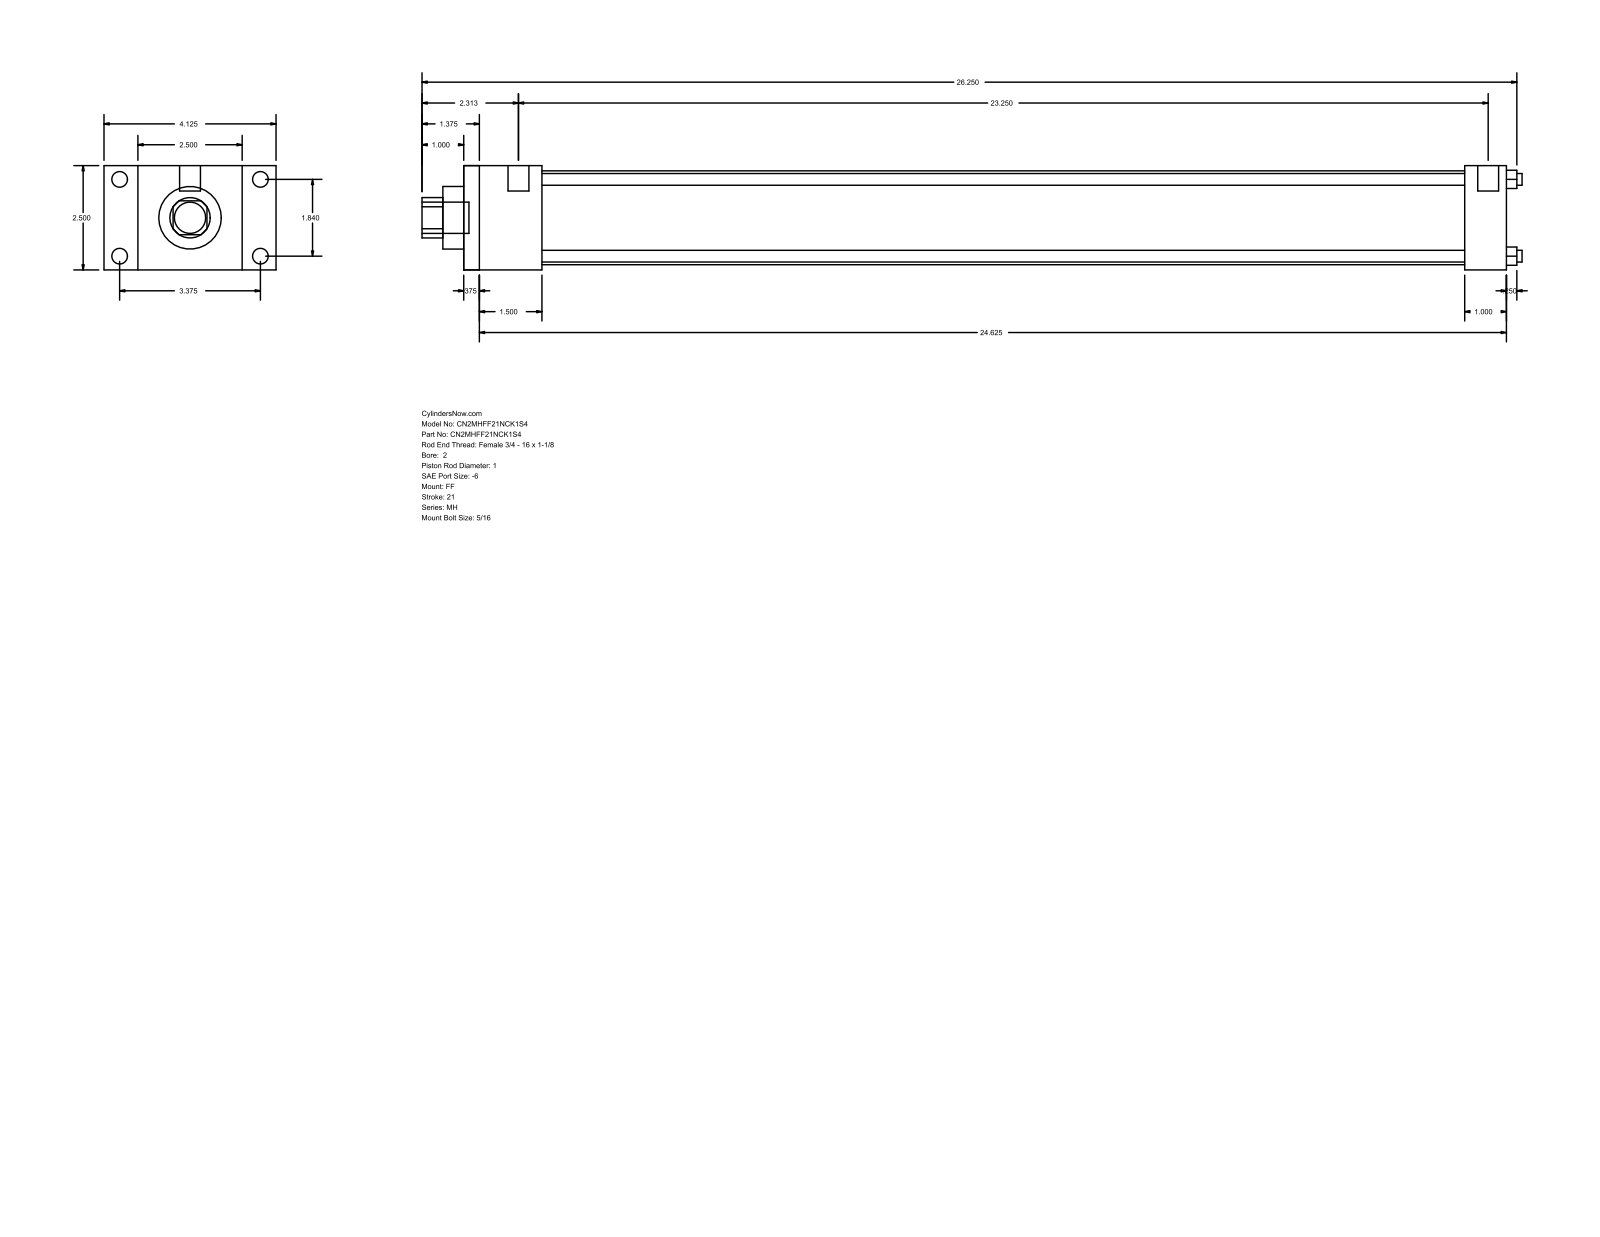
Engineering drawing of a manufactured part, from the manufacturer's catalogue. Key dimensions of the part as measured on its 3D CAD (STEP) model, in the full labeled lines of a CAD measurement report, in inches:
Part name (STEP PRODUCT): MH_FF__0200_1
STEP written by: GSSL Pune (CONFIG_CONTROL_DESIGN)
Units: inches
Bodies: 0 solids, 92 faces (64 planar, 28 cylindrical, 0 other)
Overall size (bounding box): 26.375 × 4.125 × 2.5
Round holes (diameter × count): ⌀0.281 ×4, ⌀1 ×1, ⌀1.5 ×1, ⌀2.25 ×1
Round bosses / shafts (diameter × count): ⌀0.375 ×4, ⌀0.219 ×4, ⌀0.5 ×2, ⌀0.75 ×1
Partial cylindrical surfaces — rounded edges, fillets, slot ends (radius × count): R0.484 ×1
Main face-to-face distances: 2.5, 25, 0.375, 24.625, 0.813, 1, 1.875, 24, 1.5, 23.625
Hole centre spacings: 1.301, 1.84, 2.602
